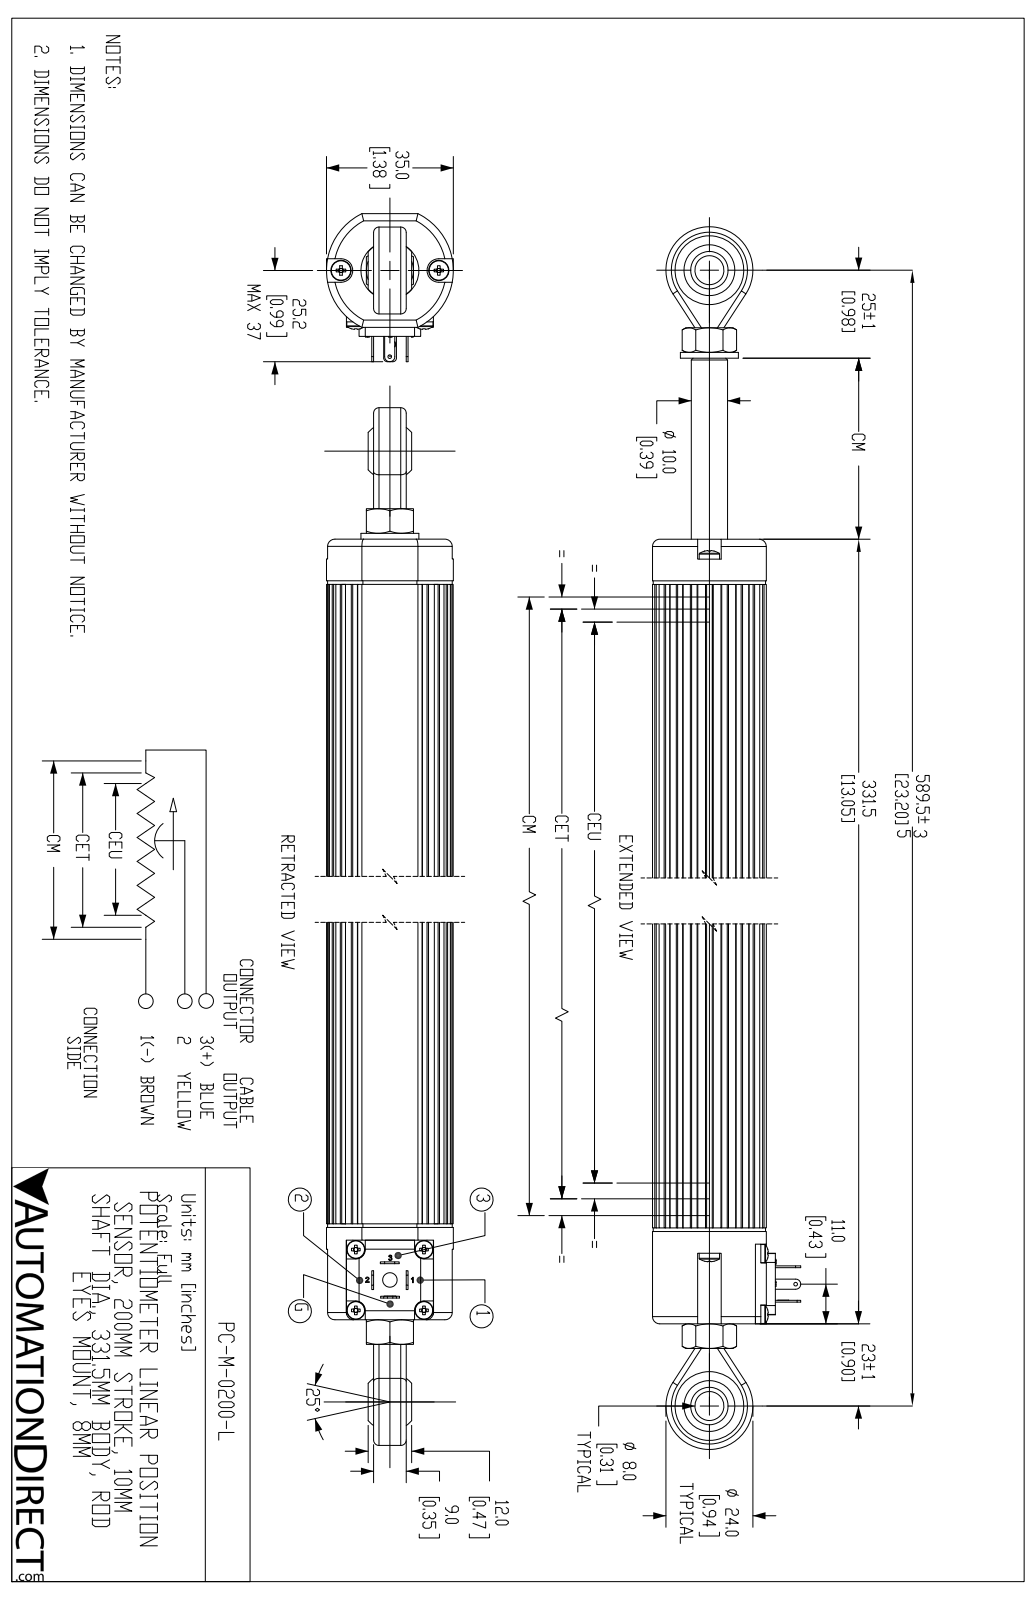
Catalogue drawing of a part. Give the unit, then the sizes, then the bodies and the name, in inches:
Units: inches
Overall size (bounding box): 16.088 × 1.61 × 1.378
Round holes (diameter × count): ⌀0.087 ×4, ⌀0.102 ×4, ⌀0.039 ×3, ⌀0.108 ×2, ⌀0.138 ×2, ⌀0.315 ×2, ⌀0.748 ×2, ⌀0.114 ×1, ⌀0.157 ×1, ⌀0.268 ×1, ⌀0.331 ×1, ⌀0.512 ×1
Round bosses / shafts (diameter × count): ⌀0.197 ×4, ⌀0.098 ×4, ⌀0.118 ×3, ⌀0.22 ×2, ⌀0.63 ×1, ⌀0.394 ×1, ⌀0.39 ×1, ⌀0.315 ×1
Partial cylindrical surfaces — rounded edges, fillets, slot ends (radius × count): R0.059 ×8, R0.039 ×5, R0.079 ×5, R0.102 ×4, R0.118 ×4, R0.055 ×2, R0.128 ×2, R0.472 ×2
Main face-to-face distances: 1.236, 0.039, 11.555, 11.516, 11.594, 0.913, 0.118, 1.118, 0.913, 12.598
Hole centre spacings: 0.496, 0.531, 0.661, 0.74, 0.993, 0.024, 0.11, 0.134
Volume: 20.45 in³ · Surface area: 115 in²
Bodies: 26 solids, 1441 faces (437 planar, 366 cylindrical, 638 other)
Part name (STEP PRODUCT): PC-M-0200-L
STEP written by: SolidWorks 2019 (AUTOMOTIVE_DESIGN)
